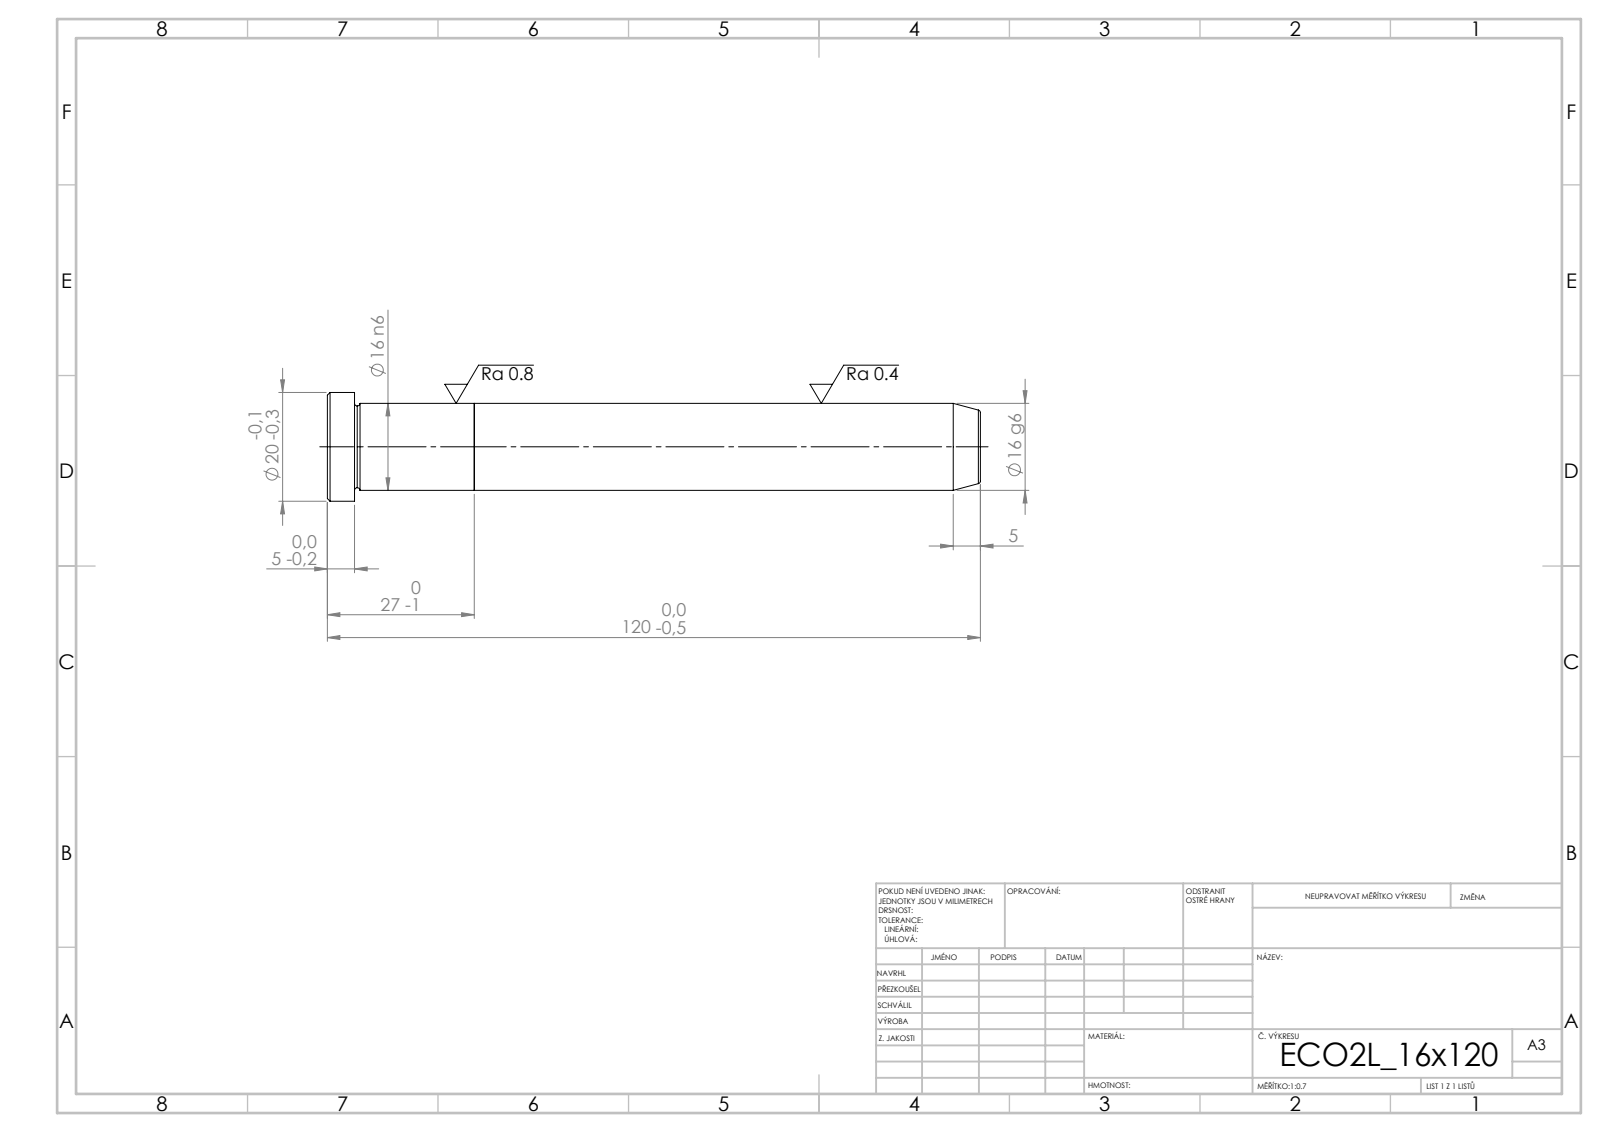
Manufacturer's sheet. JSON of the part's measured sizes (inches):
{"step_written_by": "SolidWorks 2019 (CONFIG_CONTROL_DESIGN)", "units": "inches", "bodies": {"solids": 2, "faces": 21, "planar": 5, "cylindrical": 6, "other": 10}, "overall_size": [4.724, 0.787, 0.787], "volume_in3": 1.495, "surface_area_in2": 10.93, "round_bosses_or_shafts": [[0.787, 1], [0.63, 1]], "face_to_face_distances": [1.063, 3.661, 4.724, 4.528, 0.866, 0.197]}
